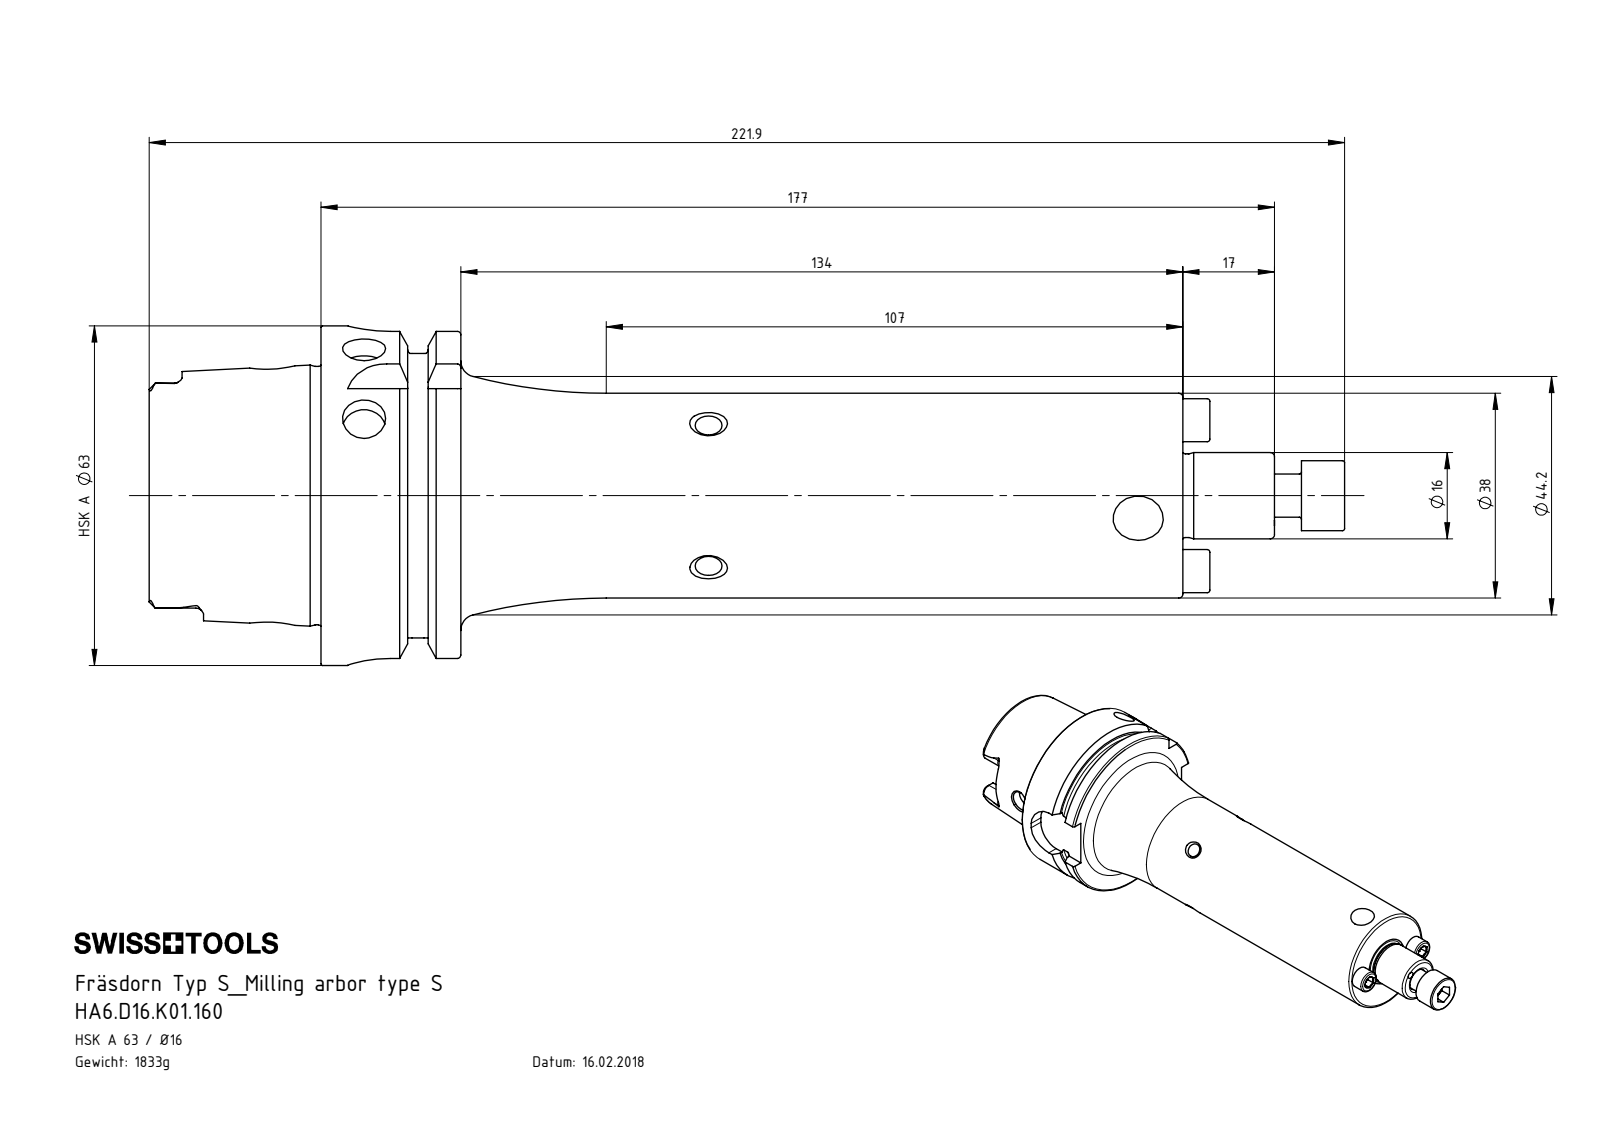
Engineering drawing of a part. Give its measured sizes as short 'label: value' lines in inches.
name: HA6.D16.K01.160; D16-ER1.002.025_A_Default; D16-ER2.001.015_B; HA6-D16.K01.160_C_Fertigbearbeitung
written by: SolidWorks 2011 (AUTOMOTIVE_DESIGN)
unit: in
bodies: 4 solids, 389 faces (91 planar, 111 cylindrical, 187 other)
size: 8.736 × 2.48 × 2.48
volume: 14.25 in³; area: 72.18 in²
holes: 3× ⌀0.098, 2× ⌀0.13, 2× ⌀0.197, 2× ⌀0.236, 2× ⌀0.315, 1× ⌀0.268, 1× ⌀0.295, 1× ⌀0.331, 1× ⌀0.335, 1× ⌀0.394, 1× ⌀0.669, 1× ⌀0.748
bosses: 3× ⌀0.315, 2× ⌀0.157, 2× ⌀0.118, 1× ⌀2.48, 1× ⌀2.163, 1× ⌀1.887, 1× ⌀1.496, 1× ⌀0.63
rounds: 6× R0.055, 4× R0.113, 4× R0.315, 2× R0.079
face distances: 1.022, 6.299, 5.278, 0.63, 0.392, 5.907, 1.256, 1.648, 2.278, 7.555
hole spacings: 0.241, 0.417, 0.551, 0.741, 0.482, 1.102, 3.23
